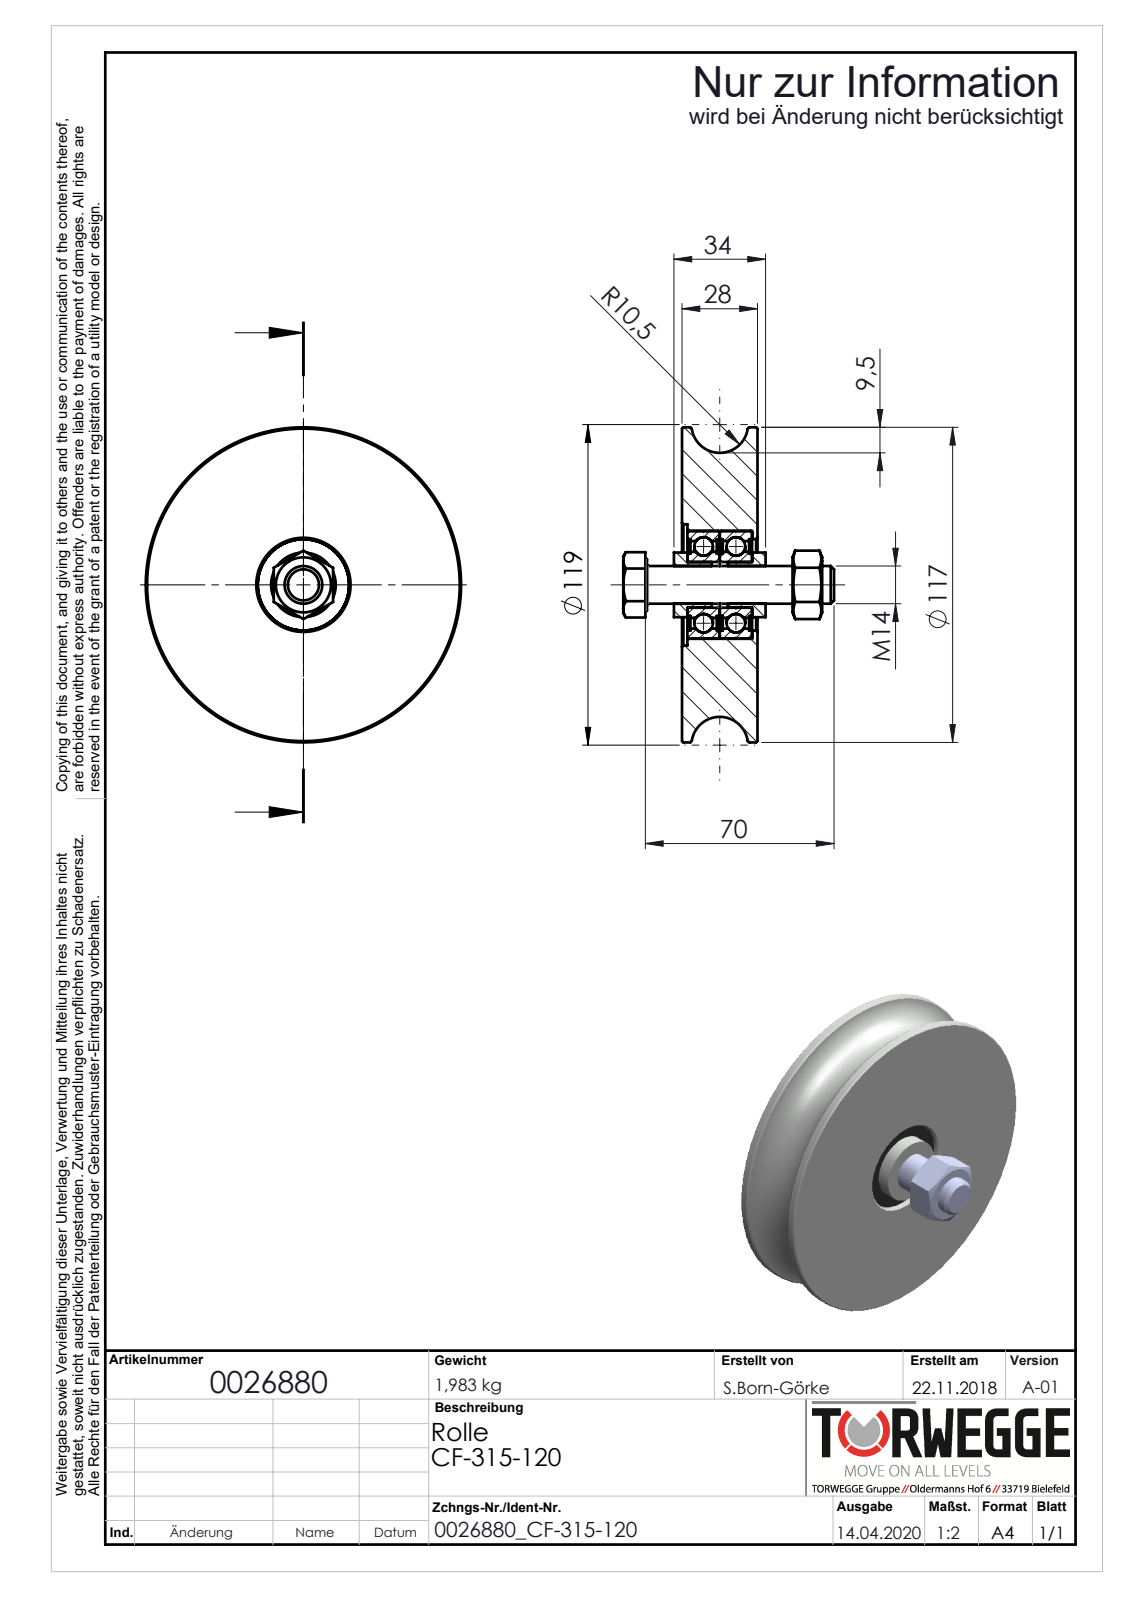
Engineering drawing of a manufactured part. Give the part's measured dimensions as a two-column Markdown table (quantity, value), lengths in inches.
| quantity | value |
| --- | --- |
| part name | 0026880 |
| STEP written by | SolidWorks 2018 (AUTOMOTIVE_DESIGN) |
| units | inches |
| bodies | 15 solids, 208 faces (52 planar, 82 cylindrical, 74 other) |
| overall size | 4.606 × 4.606 × 3.079 |
| volume | 15.64 in³ |
| surface area | 101.3 in² |
| round holes (diameter × count) | 0.466 × 1, 0.551 × 1, 0.669 × 1, 0.909 × 1, 1.28 × 1, 1.335 × 1, 1.339 × 1, 1.772 × 1 |
| round bosses / shafts (diameter × count) | 4.606 × 1, 1.575 × 1, 0.965 × 1, 0.945 × 1, 0.665 × 1 |
| main face-to-face distances | 1.102, 0.472, 0.551, 1.024, 0.079, 0.022, 0.45, 0.945, 0.428, 0.494 |
